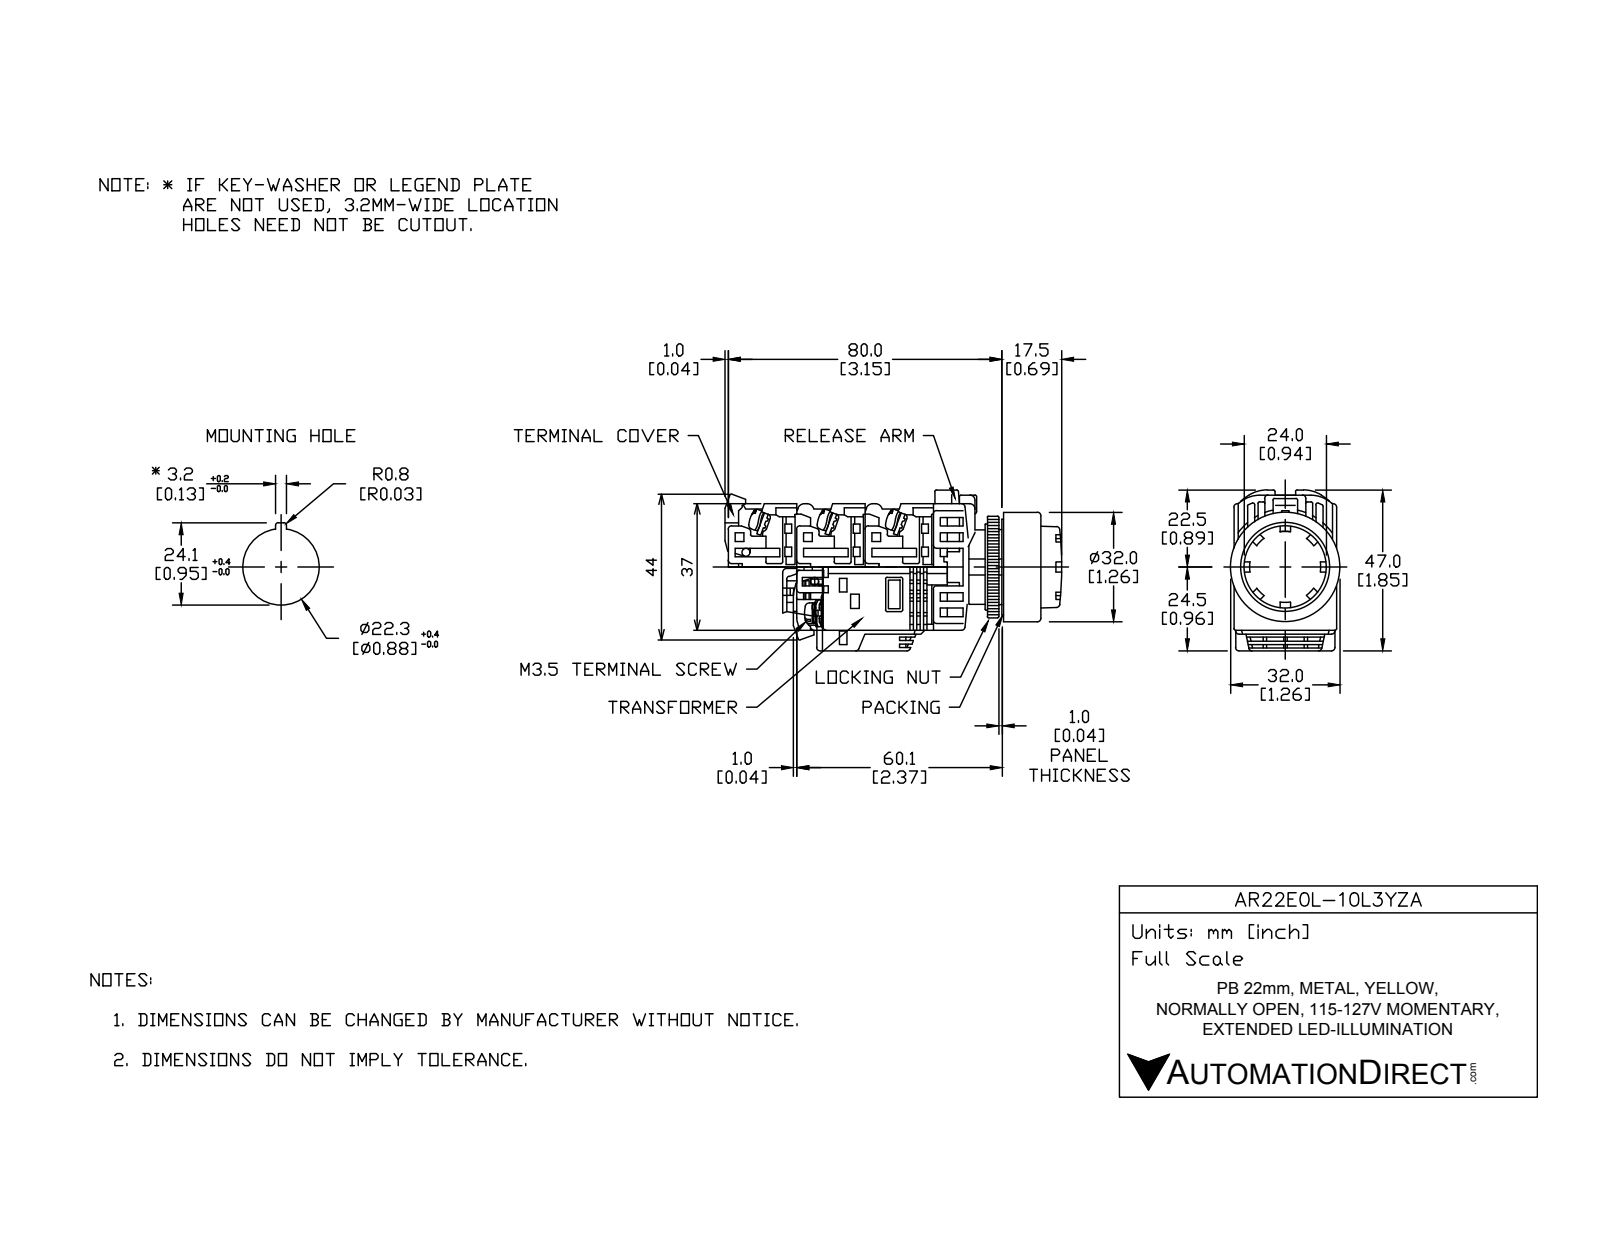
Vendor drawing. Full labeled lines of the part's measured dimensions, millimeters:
Part name (STEP PRODUCT): AR22E0L-10L3YZA
STEP written by: SolidWorks 2017 (AUTOMOTIVE_DESIGN)
Units: millimetres
Bodies: 16 solids, 451 faces (317 planar, 99 cylindrical, 35 other)
Overall size (bounding box): 79.25 × 43.81 × 32
Volume: 50 413 mm³ · Surface area: 26 207 mm²
Round holes (diameter × count): ⌀21.8 ×1, ⌀22 ×1, ⌀25 ×1, ⌀31 ×1
Round bosses / shafts (diameter × count): ⌀5 ×4, ⌀32 ×1, ⌀30.5 ×1, ⌀29.8 ×1, ⌀24 ×1, ⌀23.8 ×1, ⌀21.75 ×1, ⌀17 ×1
Partial cylindrical surfaces — rounded edges, fillets, slot ends (radius × count): R0.5 ×32, R1.75 ×8, R5 ×4, R4 ×2, R16.59 ×1, R17.59 ×1
Main face-to-face distances: 1, 18, 29, 20, 28.5, 3, 2, 21, 0.35, 7.5
